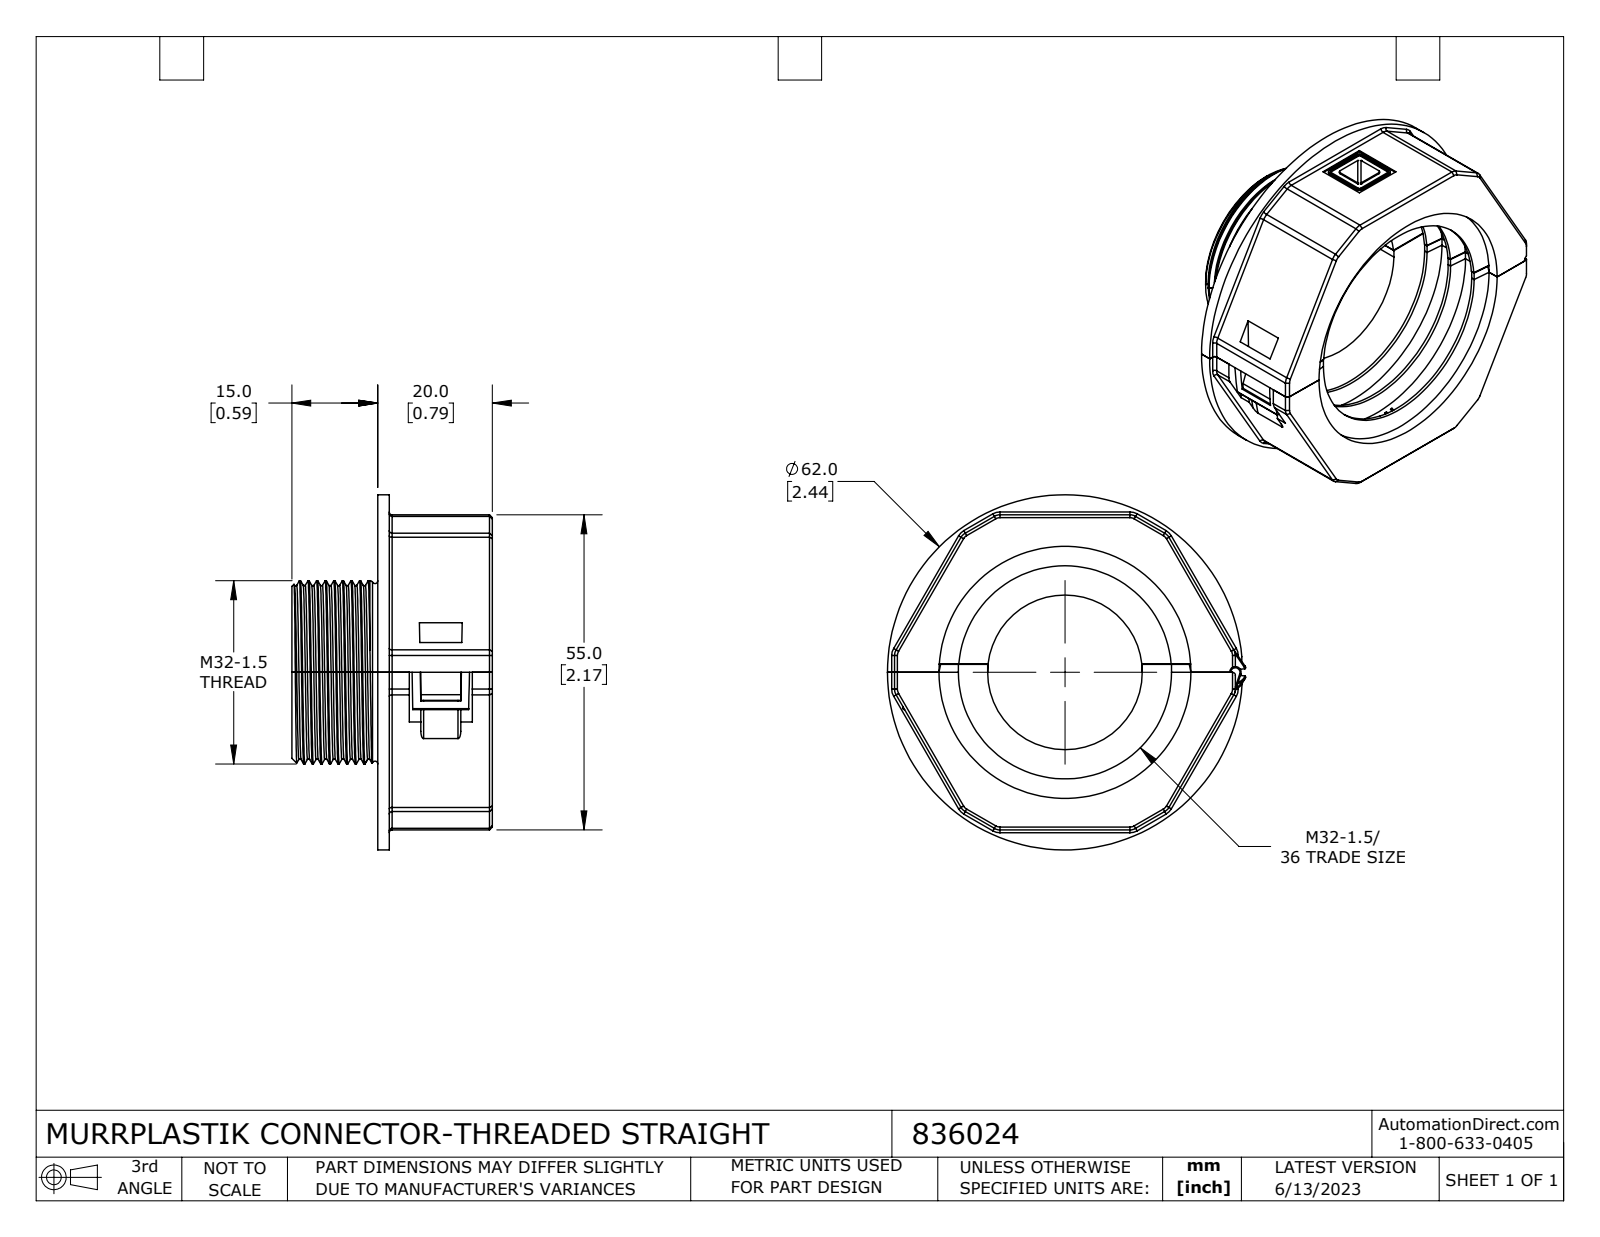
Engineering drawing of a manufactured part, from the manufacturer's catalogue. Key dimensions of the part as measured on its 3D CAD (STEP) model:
Part name (STEP PRODUCT): 836024
STEP written by: SolidWorks 2021 (CONFIG_CONTROL_DESIGN)
Units: inches
Bodies: 2 solids, 738 faces (341 planar, 163 cylindrical, 234 other)
Overall size (bounding box): 2.463 × 2.441 × 1.378
Volume: 1.741 in³ · Surface area: 28.9 in²
Round holes (diameter × count): ⌀0.079 ×1, ⌀0.197 ×1, ⌀1.063 ×1, ⌀1.465 ×1, ⌀1.732 ×1
Round bosses / shafts (diameter × count): ⌀2.441 ×1, ⌀1.26 ×1
Partial cylindrical surfaces — rounded edges, fillets, slot ends (radius × count): R0.008 ×29, R0.02 ×21, R0.079 ×19, R0.013 ×4, R0.016 ×4, R0.025 ×4, R0.098 ×1, R0.539 ×1
Main face-to-face distances: 0.669, 0.118, 2.165, 0.787, 1.083, 0.709, 0.039, 0.079, 2.343, 0.059
Hole centre spacings: 1.171
